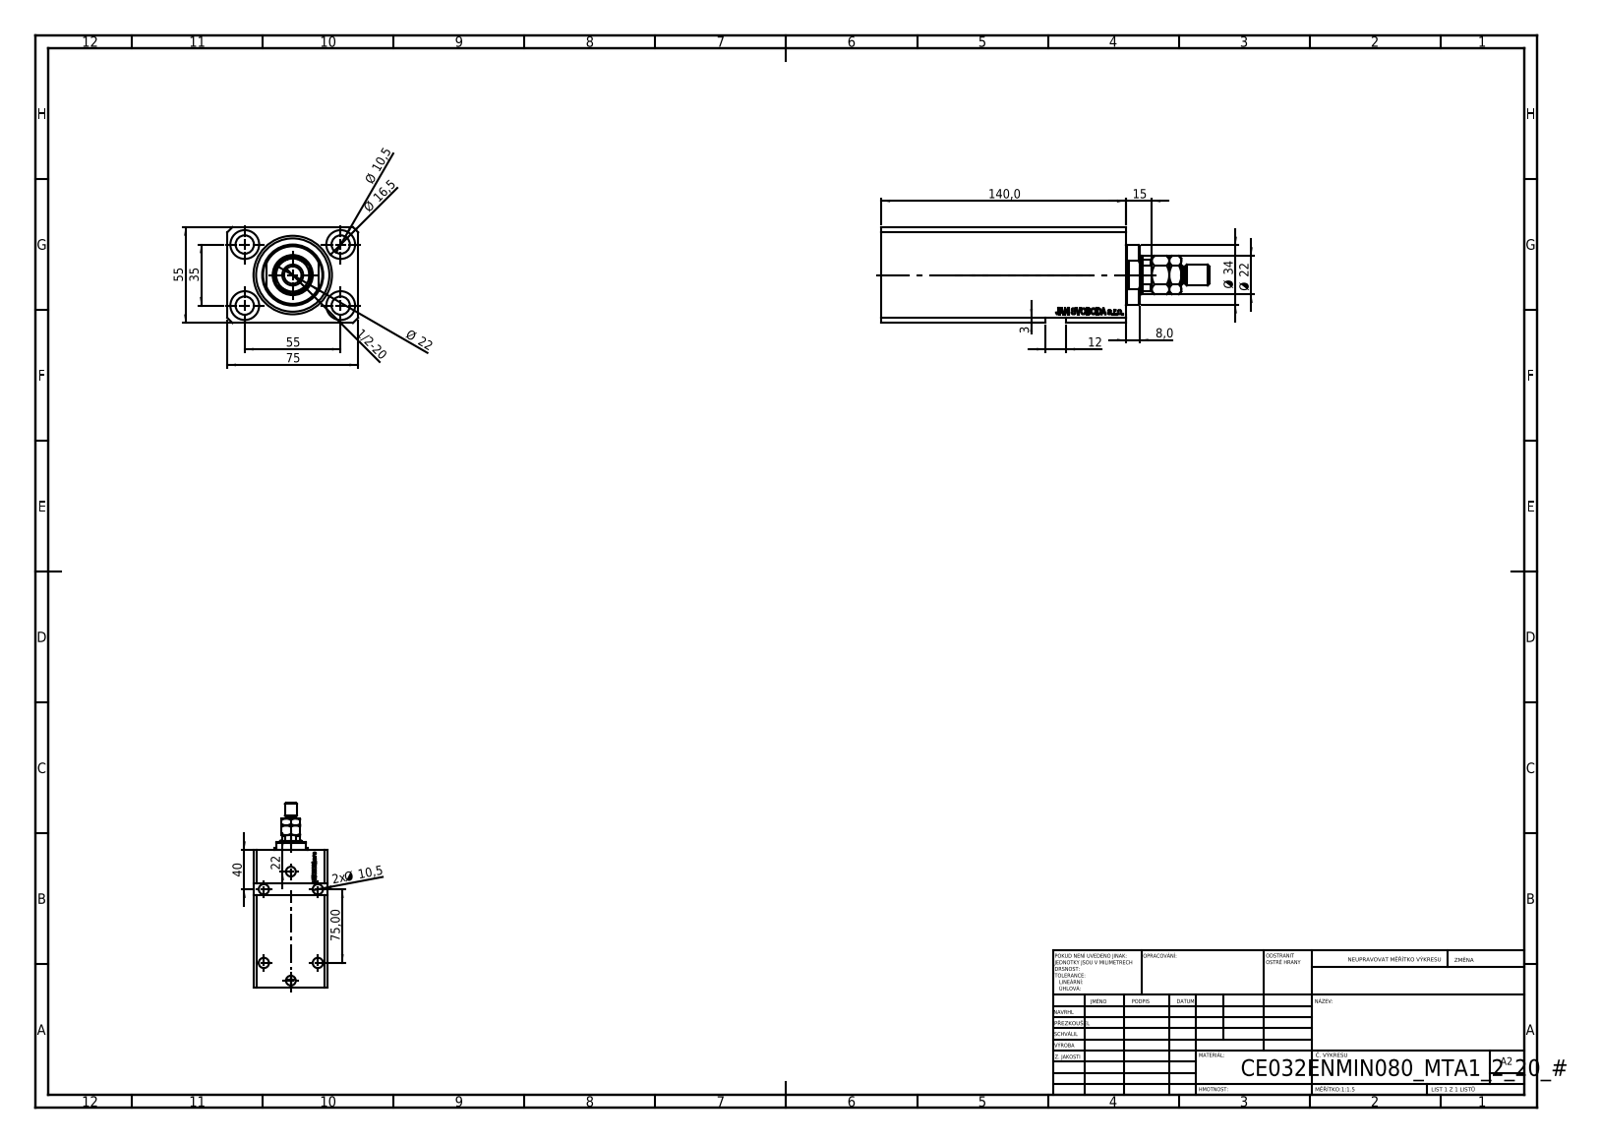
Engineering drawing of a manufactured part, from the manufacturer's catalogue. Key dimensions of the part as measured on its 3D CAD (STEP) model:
Part name (STEP PRODUCT): V250CE_E_Body; V250CE_C_VCP; V250CE_VC_E; MTA
STEP written by: SolidWorks 2019 (CONFIG_CONTROL_DESIGN)
Units: millimetres
Bodies: 4 solids, 963 faces (453 planar, 108 cylindrical, 402 other)
Overall size (bounding box): 188 × 75 × 55
Volume: 476 184 mm³ · Surface area: 104 344 mm²
Round holes (diameter × count): ⌀10.5 ×9, ⌀1.25 ×4, ⌀16.5 ×4, ⌀10 ×2, ⌀13.16 ×2, ⌀20 ×2, ⌀22 ×1, ⌀32 ×1, ⌀45 ×1
Round bosses / shafts (diameter × count): ⌀34 ×1, ⌀12 ×1, ⌀10 ×1
Partial cylindrical surfaces — rounded edges, fillets, slot ends (radius × count): R10.5 ×1
Main face-to-face distances: 55, 75, 15, 140, 125, 9.9, 115.1, 130.1, 19, 11
Hole centre spacings: 32.6, 32.87, 55, 96.98, 32.58, 35, 65.19, 75
